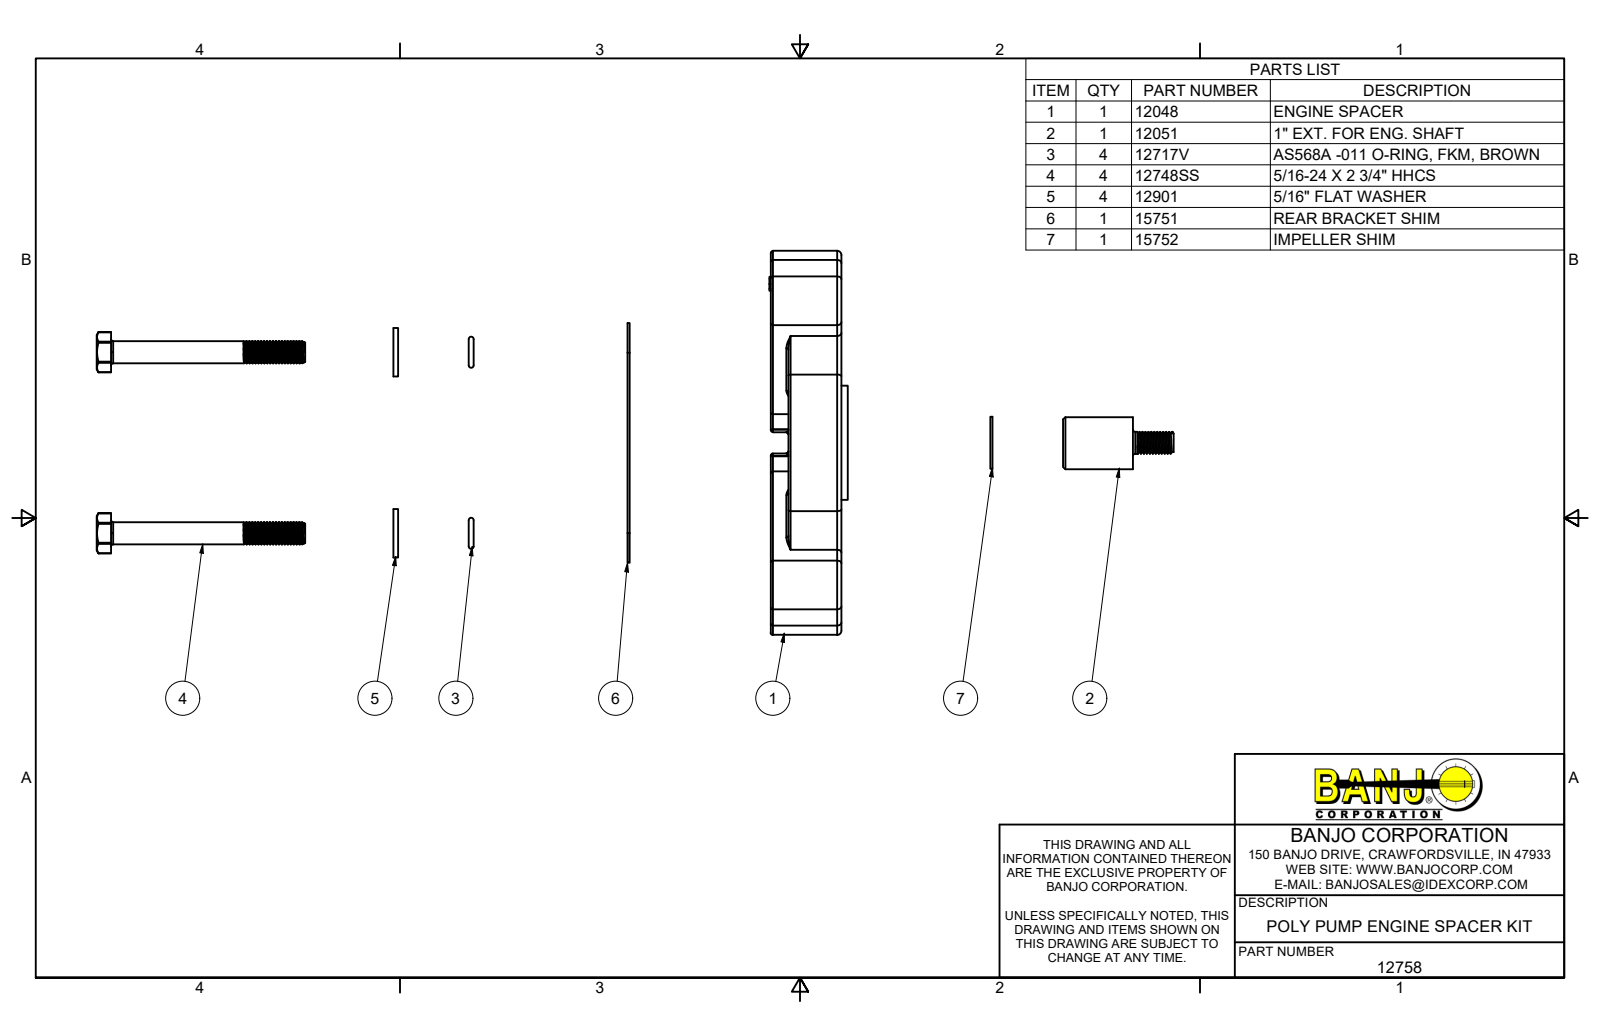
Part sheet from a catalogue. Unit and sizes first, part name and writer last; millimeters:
Units: millimetres
Overall size (bounding box): 138.1 × 138.1 × 82.7
Round holes (diameter × count): ⌀8 ×4, ⌀8.2 ×4, ⌀8.7 ×4, ⌀10.3 ×4, ⌀22.2 ×4, ⌀6.8 ×1, ⌀12.7 ×1, ⌀35.1 ×1, ⌀38.4 ×1, ⌀41.3 ×1, ⌀41.4 ×1, ⌀114.4 ×1
Round bosses / shafts (diameter × count): ⌀7 ×80, ⌀8 ×5, ⌀21.6 ×4, ⌀17.5 ×4, ⌀41 ×1, ⌀19.1 ×1, ⌀18.7 ×1, ⌀6.7 ×1
Partial cylindrical surfaces — rounded edges, fillets, slot ends (radius × count): R0.8 ×38, R6.4 ×16, R12.7 ×16, R3.5 ×8, R1.5 ×4, R7.2 ×4, R10.7 ×4, R31.9 ×1
Main face-to-face distances: 0.8, 25.4, 26.2, 3.2, 22.2, 23, 6.4, 19.1, 15.9, 7.1
Hole centre spacings: 87.7, 28.6, 46, 65.1, 74.6, 105.5, 120.7, 92.1
Volume: 292 700 mm³ · Surface area: 84 970 mm²
Bodies: 16 solids, 1344 faces (199 planar, 530 cylindrical, 615 other)
Part name (STEP PRODUCT): 12758; 12048; 15751; 12051 (+4 more)
STEP written by: Autodesk Inventor 2019 (AUTOMOTIVE_DESIGN)
